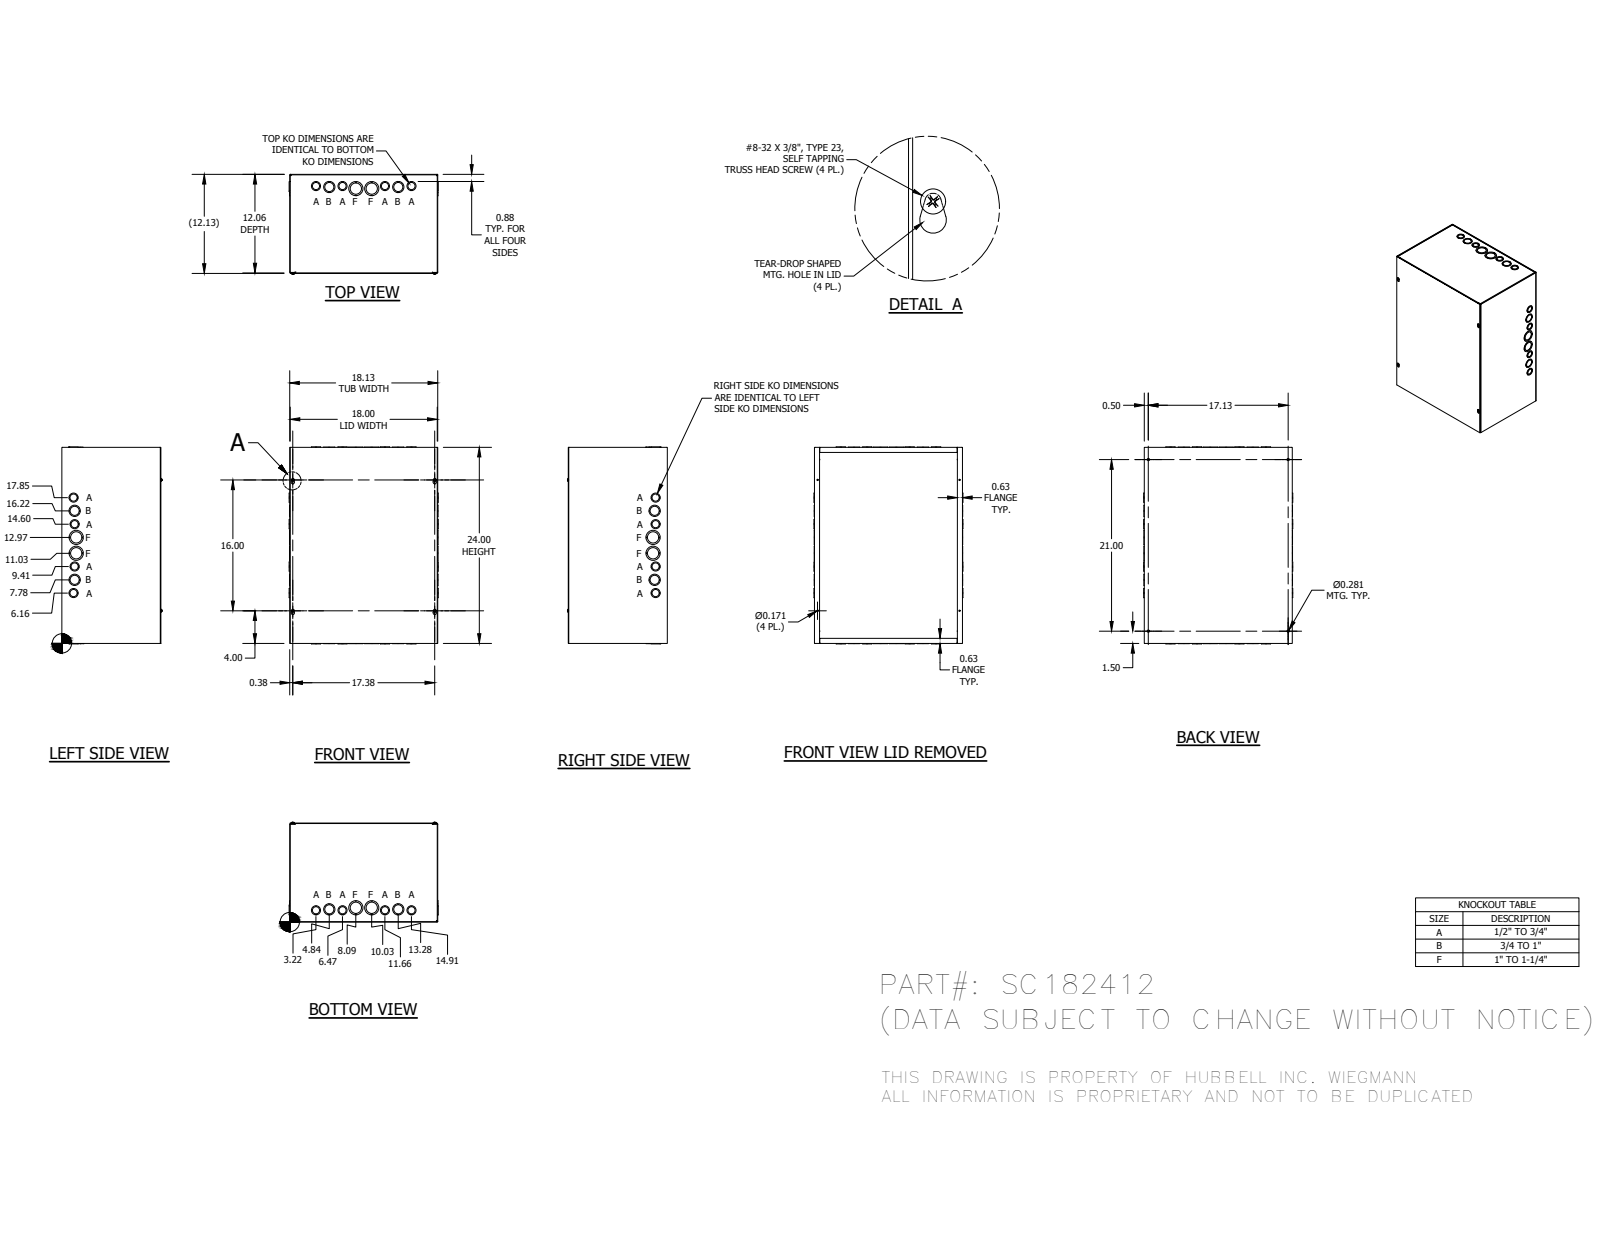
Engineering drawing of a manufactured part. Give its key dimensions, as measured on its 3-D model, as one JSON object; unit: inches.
{"part_name": "SC182412BLR; SC1812TB; SC1824LPA; 34056 (+1 more)", "step_written_by": "Autodesk Inventor 2014 (AUTOMOTIVE_DESIGN)", "units": "inches", "bodies": {"solids": 37, "faces": 1167, "planar": 859, "cylindrical": 240, "other": 68}, "overall_size": [24.125, 18.25, 12.225], "round_holes": [[1.125, 14], [0.875, 10], [1.375, 8], [0.171, 4], [0.281, 4], [1.75, 4]], "round_bosses_or_shafts": [[0.384, 4], [0.164, 4]], "partial_cylinders_radius": [[0.031, 12], [0.094, 12], [0.125, 4], [0.203, 4]], "face_to_face_distances": [0.063, 12.063, 18.063, 12, 12.125, 23.937, 18, 18.125, 24, 23.875], "hole_center_spacings": [1.63, 1.63, 1.655, 2.503, 3.25, 3.256, 3.579, 4.885]}
